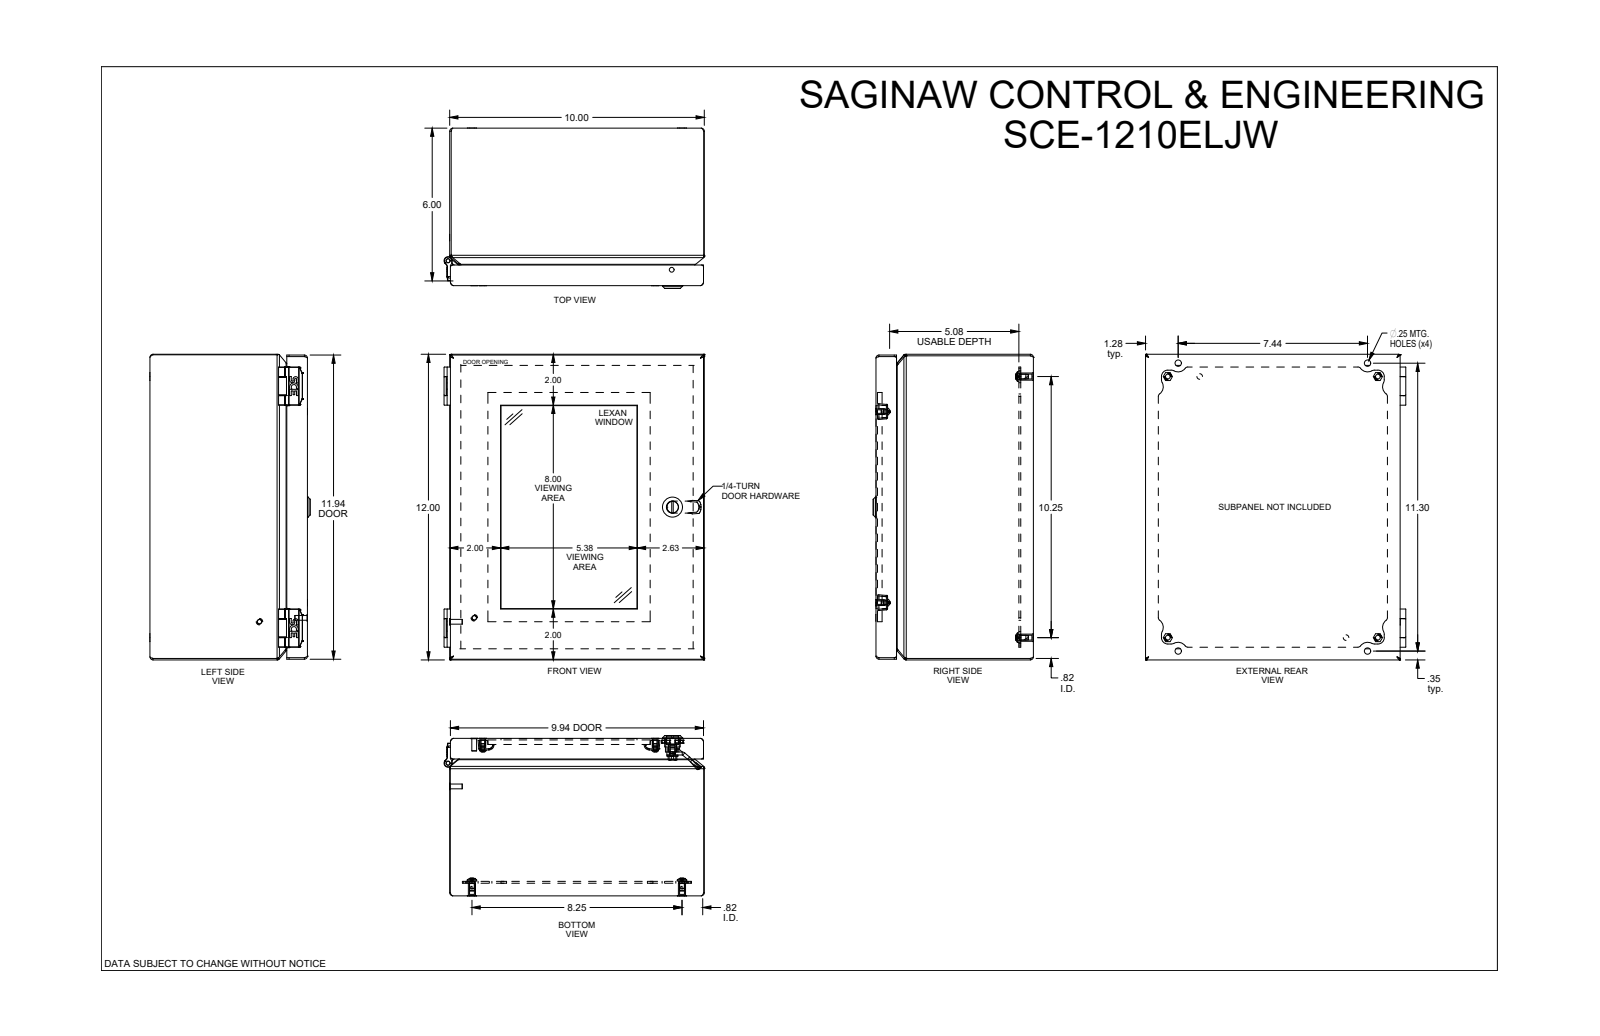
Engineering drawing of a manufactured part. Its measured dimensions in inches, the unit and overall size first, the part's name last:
Units: inches
Overall size (bounding box): 12.06 × 10.223 × 6.296
Round holes (diameter × count): ⌀0.17 ×4, ⌀0.19 ×4, ⌀0.25 ×4, ⌀0.284 ×4, ⌀0.158 ×3, ⌀0.02 ×2, ⌀0.1 ×2, ⌀0.218 ×2, ⌀0.266 ×2, ⌀0.196 ×1, ⌀0.2 ×1, ⌀0.239 ×1
Round bosses / shafts (diameter × count): ⌀0.188 ×6, ⌀0.479 ×4, ⌀0.373 ×4, ⌀0.28 ×4, ⌀0.16 ×4, ⌀0.26 ×2, ⌀0.256 ×2, ⌀0.237 ×2
Partial cylindrical surfaces — rounded edges, fillets, slot ends (radius × count): R0.03 ×28, R0.025 ×24, R0.013 ×22, R0.05 ×16, R0.125 ×14, R0.25 ×14, R0.01 ×10, R0.06 ×10
Main face-to-face distances: 0.059, 10.001, 0.06, 12.001, 0.571, 0.512, 0.496, 0.437, 0.075, 6.066
Hole centre spacings: 8.31, 0.06, 1.25, 5.138, 7, 8.25, 9.397, 9.5
Volume: 53.24 in³ · Surface area: 1 392 in²
Bodies: 35 solids, 1095 faces (410 planar, 349 cylindrical, 336 other)
Part name (STEP PRODUCT): SCE-1210ELJW
STEP written by: SolidWorks 2019 (AUTOMOTIVE_DESIGN)
